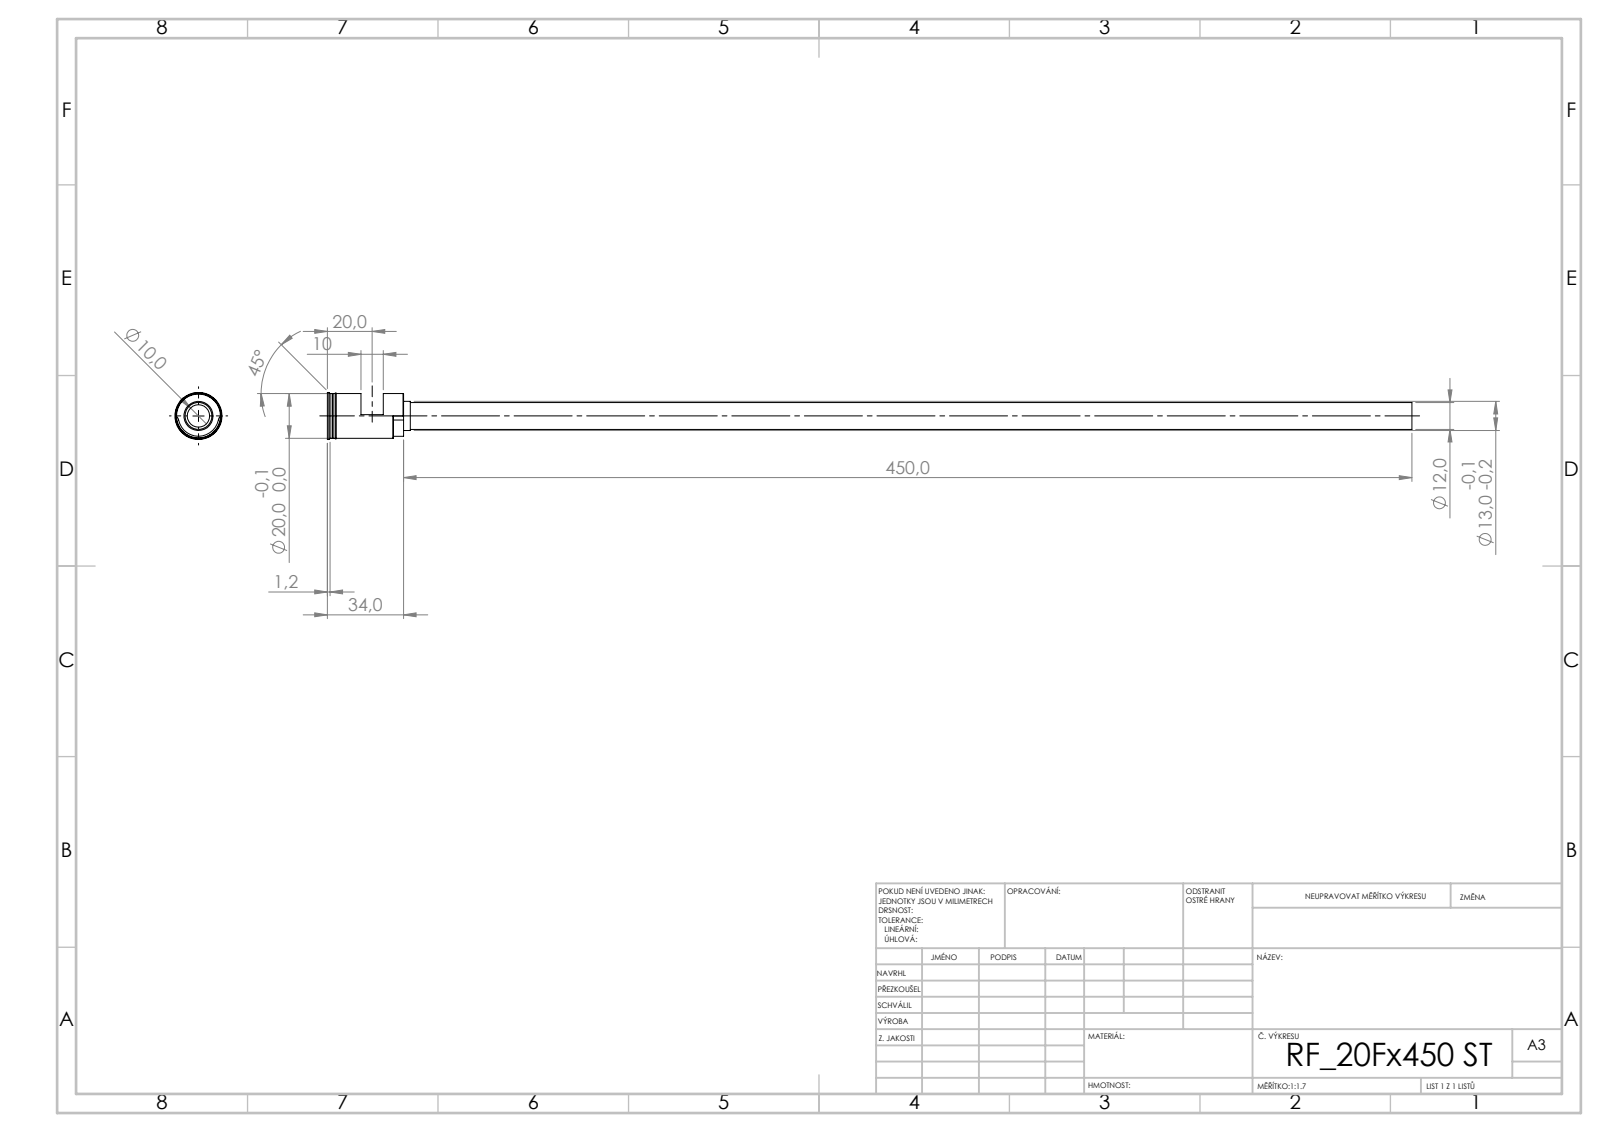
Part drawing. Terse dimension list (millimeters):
written by: SolidWorks 2019 (CONFIG_CONTROL_DESIGN)
unit: mm
bodies: 1 solid, 55 faces (24 planar, 19 cylindrical, 12 other)
size: 484 × 21 × 21
volume: 23 150 mm³; area: 34 520 mm²
holes: 1× ⌀10
bosses: 1× ⌀21, 1× ⌀20, 1× ⌀19.8, 1× ⌀13, 1× ⌀12
rounds: 2× R3, 1× R9.05
face distances: 13, 19, 32, 2, 34, 15, 9, 10, 23, 25
